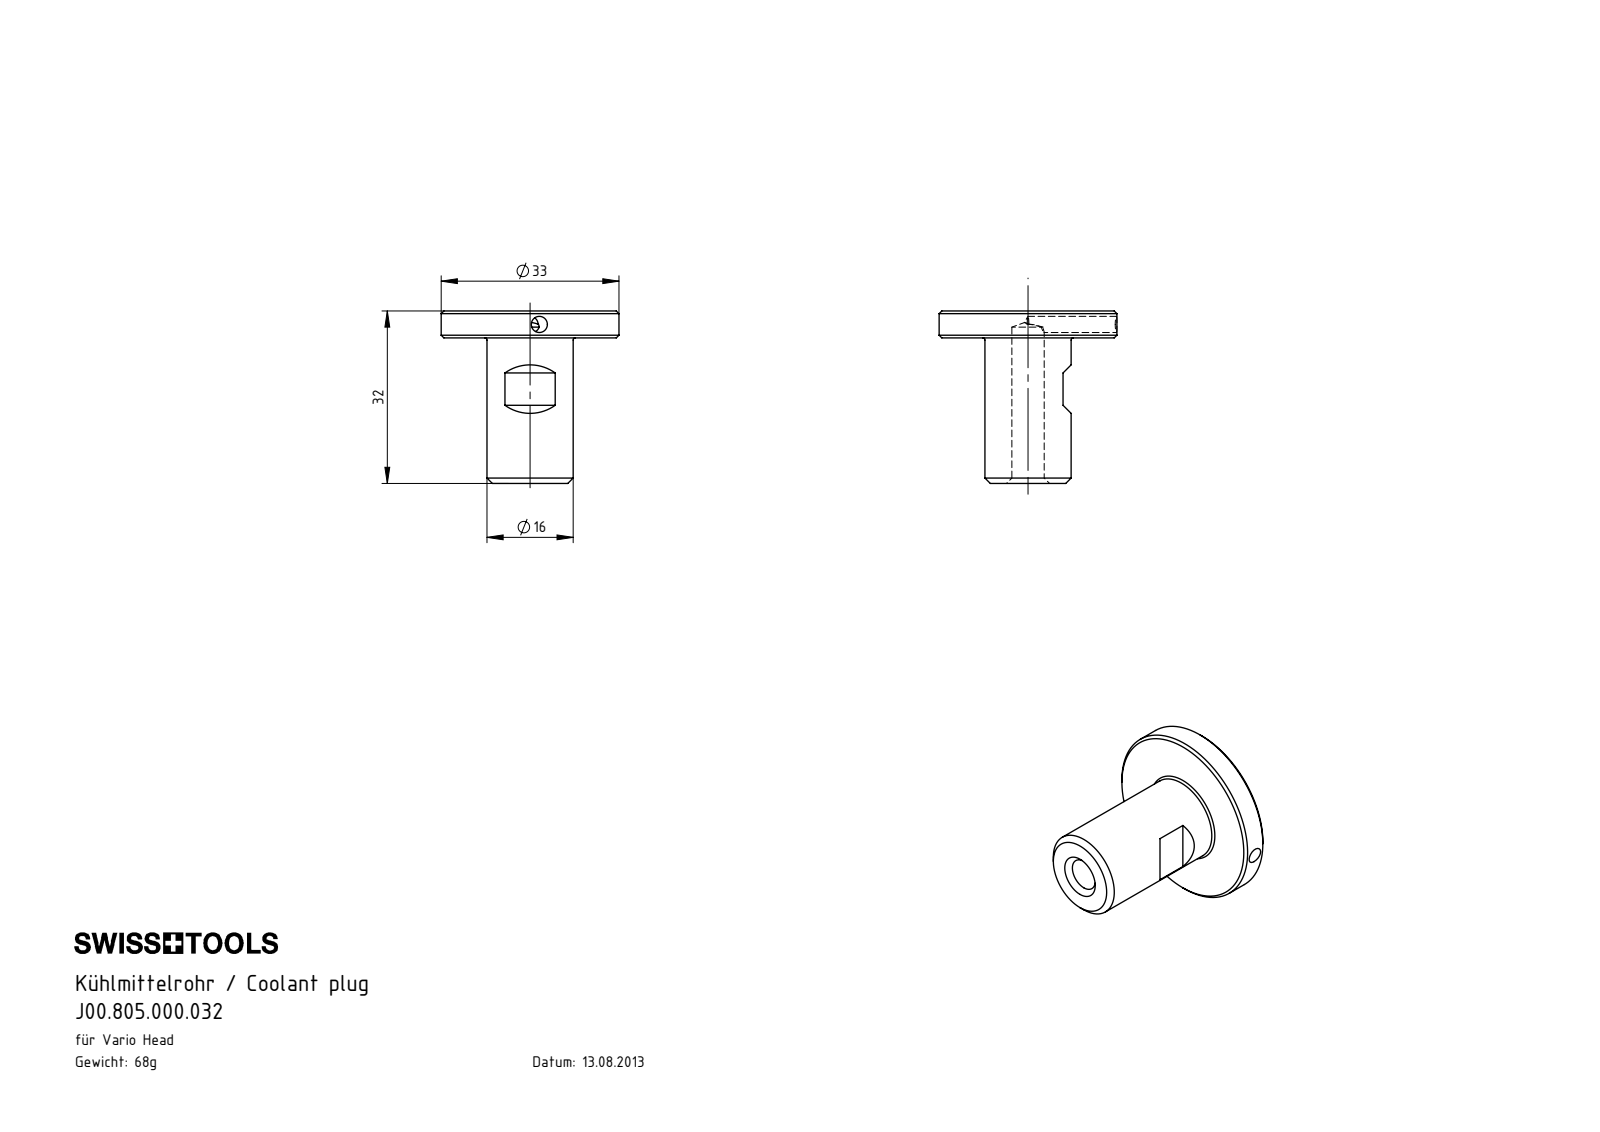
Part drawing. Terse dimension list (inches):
name: J00.805.000.032
written by: SolidWorks 2022 (CONFIG_CONTROL_DESIGN)
unit: in
bodies: 1 solid, 28 faces (6 planar, 8 cylindrical, 14 other)
size: 1.299 × 1.299 × 1.26
volume: 0.527 in³; area: 6.439 in²
holes: 1× ⌀0.118, 1× ⌀0.236
bosses: 1× ⌀1.299, 1× ⌀0.63
face distances: 0.197, 1.063, 1.26
